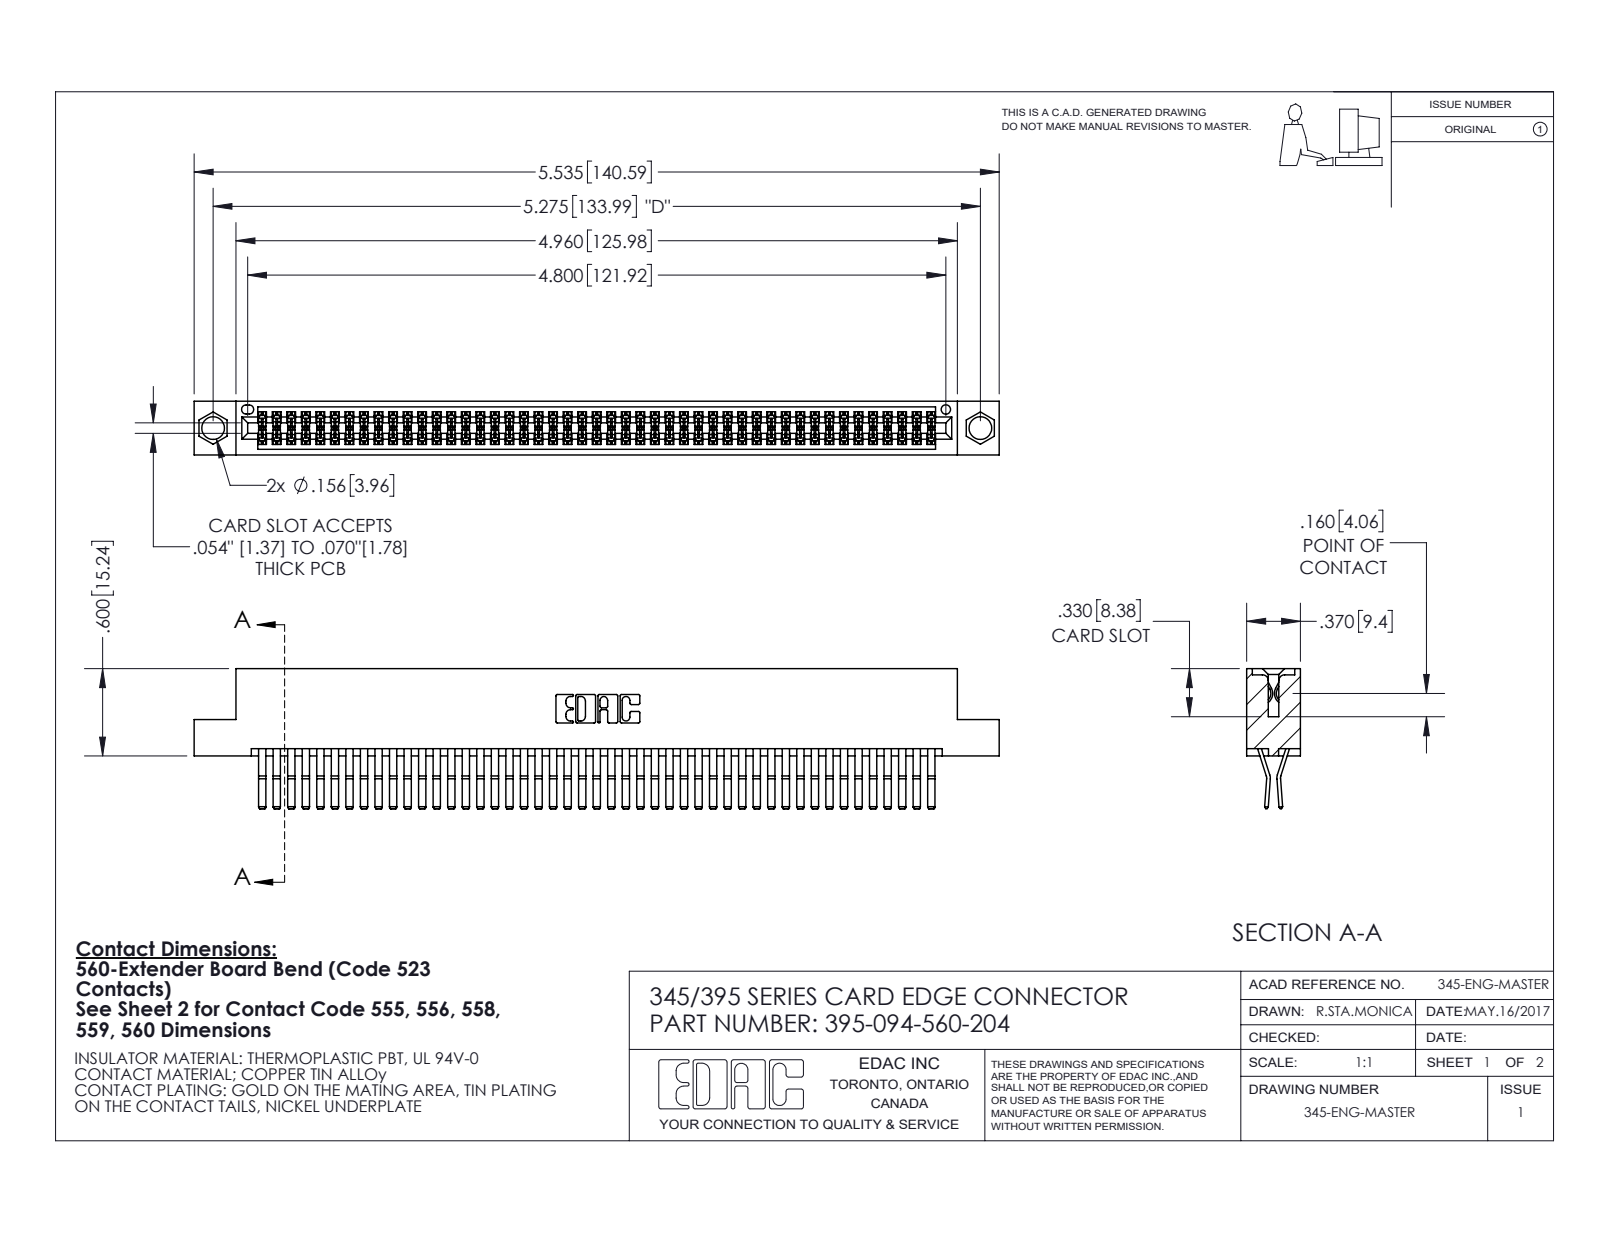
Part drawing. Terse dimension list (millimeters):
name: 345 Part_Flush Mounting Lugs - 0.156 Dia-TI; 345-292-001_560 Tail; 395-094-560-204
written by: SolidWorks 2020 (CONFIG_CONTROL_DESIGN)
unit: mm
bodies: 95 solids, 5028 faces (3196 planar, 1832 cylindrical, 0 other)
size: 140.6 × 24.4 × 9.4
volume: 14 200 mm³; area: 22 540 mm²
holes: 2× ⌀4, 1× ⌀1.6
rounds: 141× R0.2, 22× R0.3, 6× R0.2, 6× R0.8, 3× R0.7, 2× R0.3, 2× R0.4, 2× R0.5
face distances: 0.6, 7.6, 1.8, 5.1, 9.4, 2.5, 6.9, 5.7, 4.4, 3.8
hole spacings: 6.9, 128, 134
